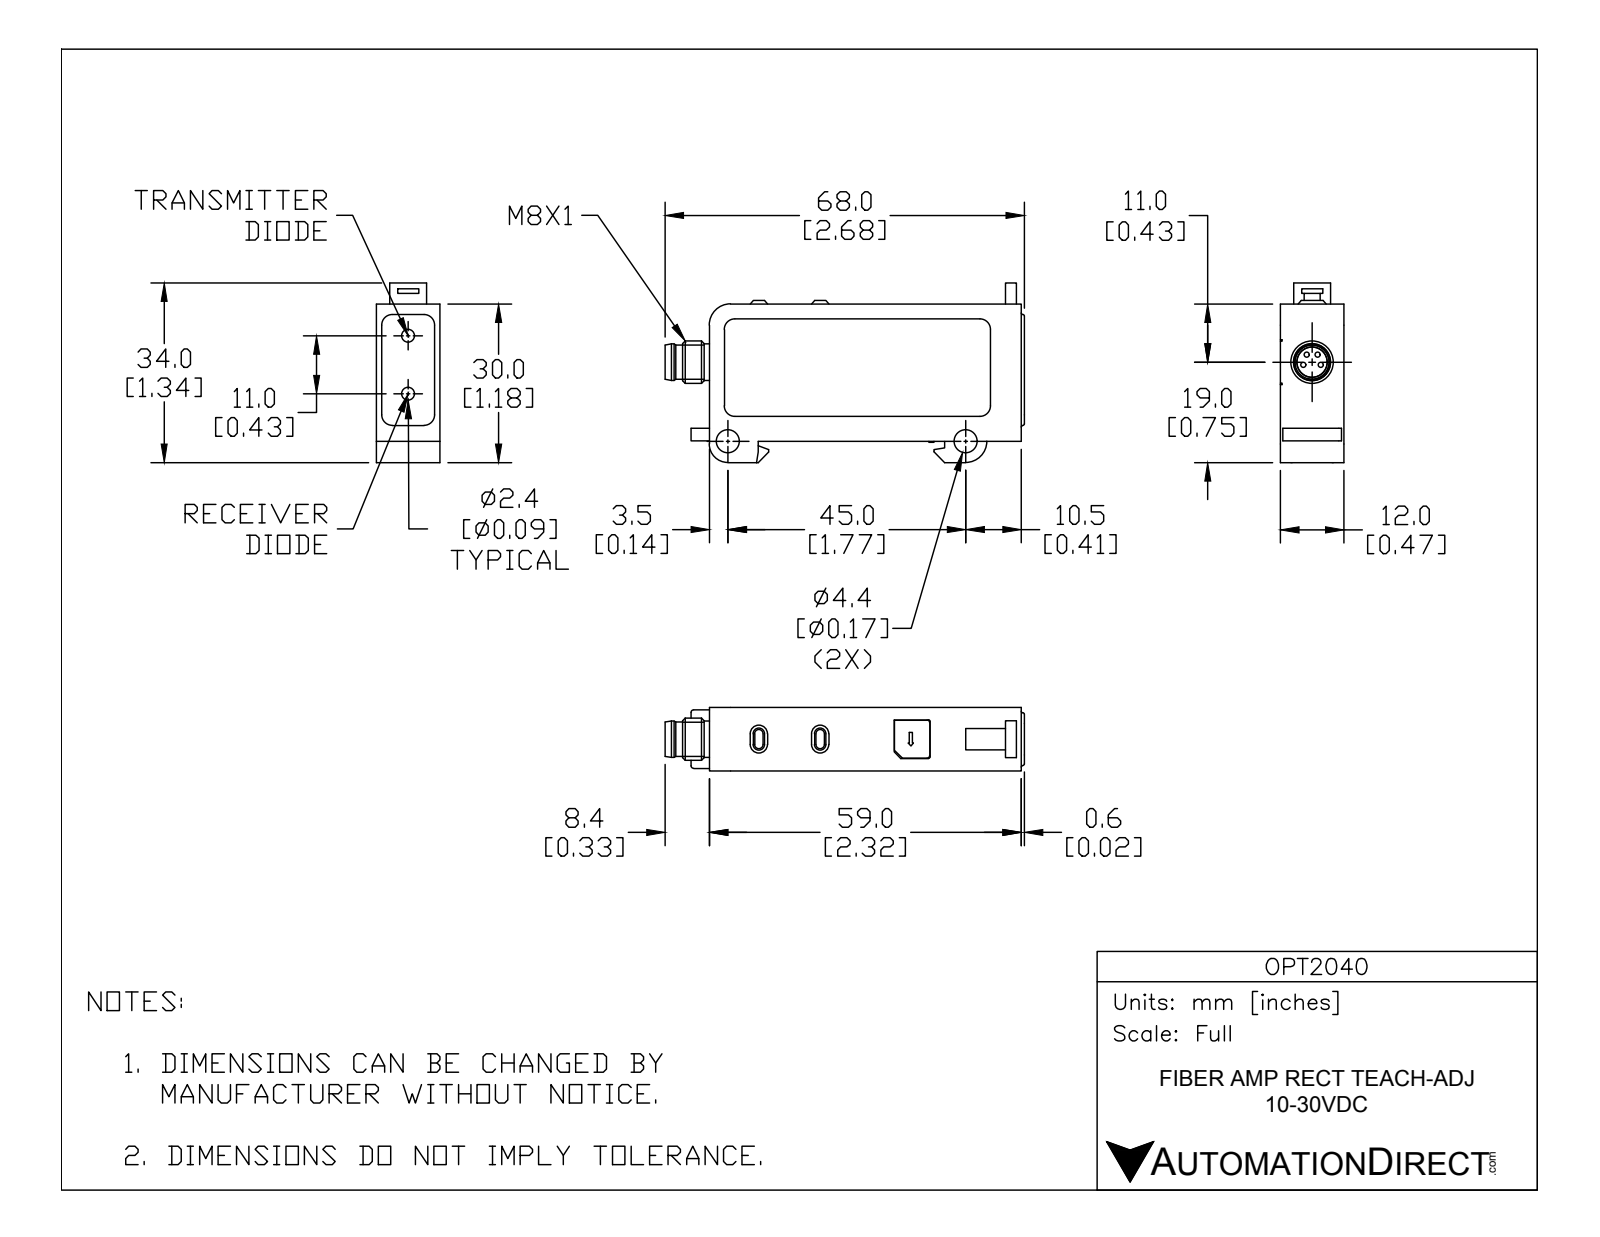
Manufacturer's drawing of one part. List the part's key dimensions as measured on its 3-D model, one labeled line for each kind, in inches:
Part name (STEP PRODUCT): OPT2040
STEP written by: SolidWorks 2014 (AUTOMOTIVE_DESIGN)
Units: inches
Bodies: 1 solid, 413 faces (223 planar, 87 cylindrical, 103 other)
Overall size (bounding box): 2.677 × 1.339 × 0.472
Volume: 1.132 in³ · Surface area: 10.65 in²
Round holes (diameter × count): ⌀0.094 ×2, ⌀0.173 ×2, ⌀0.224 ×1, ⌀0.227 ×1
Round bosses / shafts (diameter × count): ⌀0.039 ×4, ⌀0.315 ×1, ⌀0.272 ×1, ⌀0.256 ×1
Partial cylindrical surfaces — rounded edges, fillets, slot ends (radius × count): R0.012 ×10, R0.03 ×9, R0.079 ×6, R0.089 ×5, R0.016 ×4, R0.02 ×4, R0.106 ×3, R0.039 ×2
Main face-to-face distances: 0.465, 0.457, 0.472, 1.024, 2.346, 0.098, 0.157, 0.925, 0.059, 1.181
Hole centre spacings: 0.197, 0.236, 0.433, 1.772
